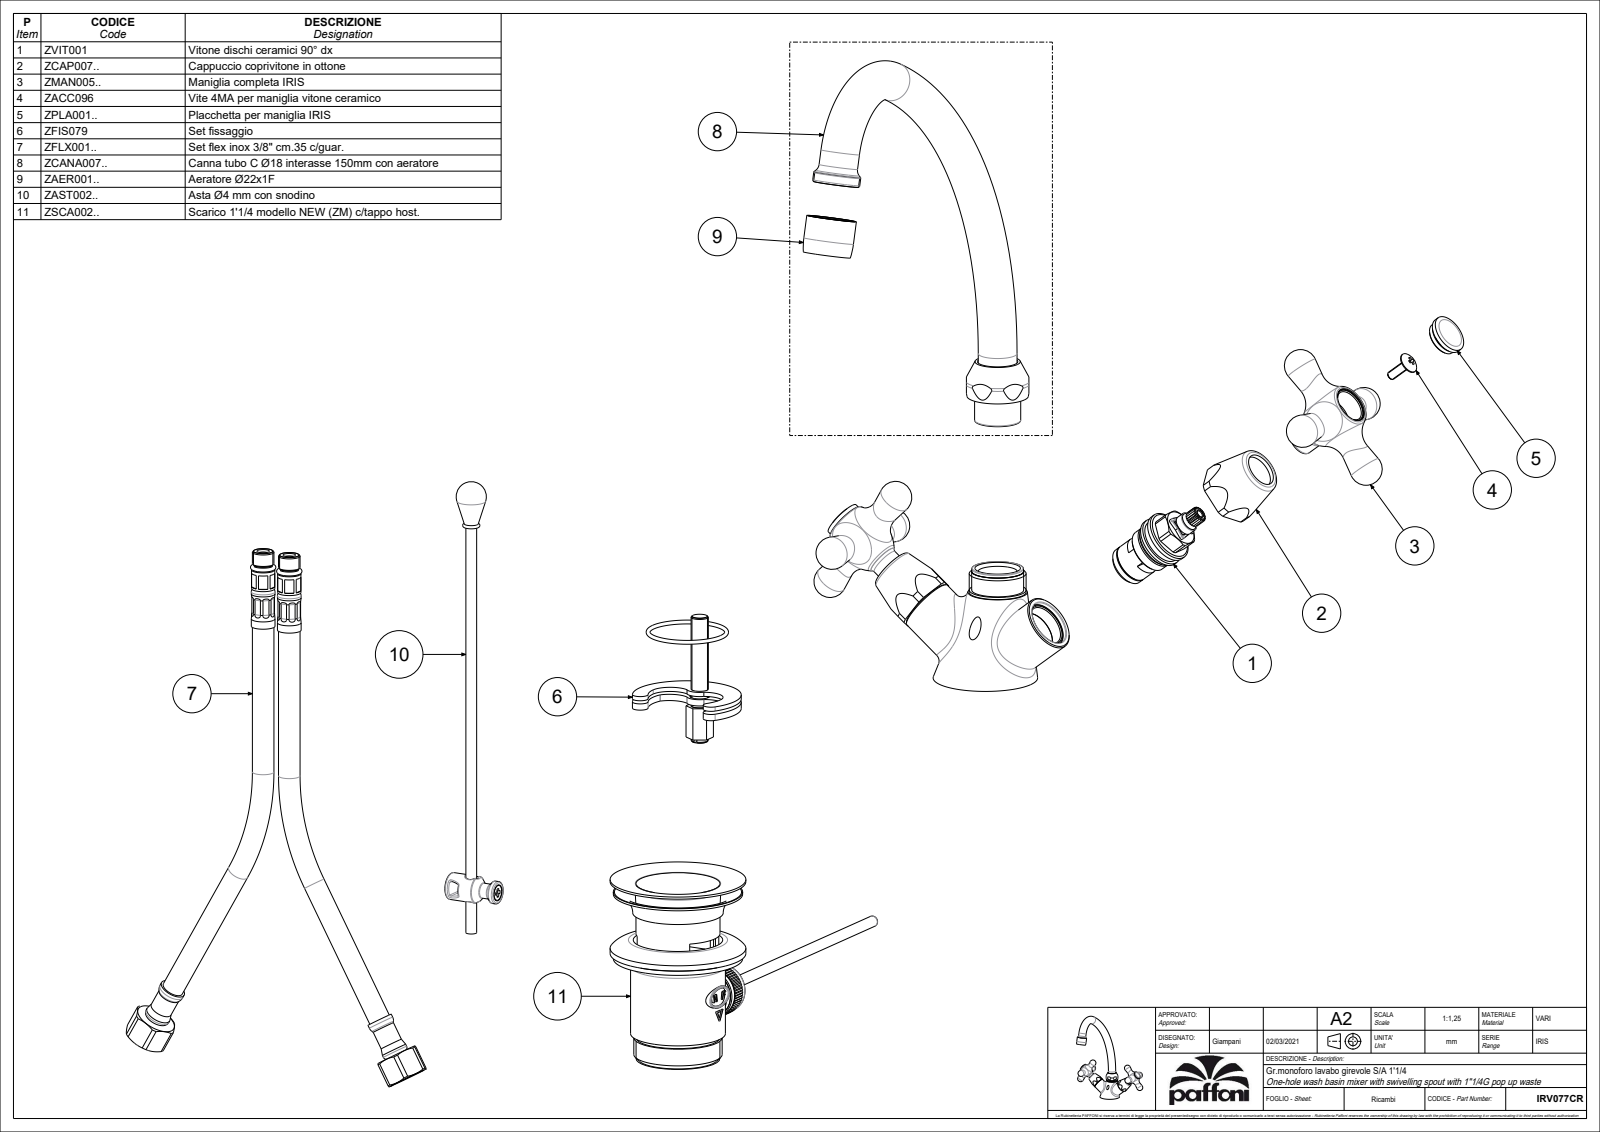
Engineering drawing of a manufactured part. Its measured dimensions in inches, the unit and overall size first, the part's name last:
Units: inches
Overall size (bounding box): 8.996 × 7.513 × 7.243
Round holes (diameter × count): ⌀0.008 ×777, ⌀0.354 ×4, ⌀0.827 ×3, ⌀0.181 ×2, ⌀0.346 ×2, ⌀0.406 ×2, ⌀0.433 ×2, ⌀0.618 ×2, ⌀0.646 ×2, ⌀0.748 ×2, ⌀0.906 ×2, ⌀0.217 ×1
Round bosses / shafts (diameter × count): ⌀0.709 ×4, ⌀1.035 ×2, ⌀0.732 ×2, ⌀0.693 ×2, ⌀0.531 ×2, ⌀0.374 ×2, ⌀0.323 ×2, ⌀0.291 ×2
Partial cylindrical surfaces — rounded edges, fillets, slot ends (radius × count): R0.004 ×34, R0.02 ×4, R0.039 ×4, R0.197 ×2, R0.366 ×2, R0.37 ×2, R0.571 ×2
Main face-to-face distances: 0.051, 0.039, 0.177, 1.043, 1.035, 0.287, 0.291, 0.858, 0.185, 0.669
Hole centre spacings: 0.059, 0.138, 0.079, 0.02, 0.197, 0.118, 0.039, 0.157
Volume: 9.039 in³ · Surface area: 128.6 in²
Bodies: 3 solids, 2620 faces (560 planar, 1786 cylindrical, 274 other)
Part name (STEP PRODUCT): IRV077CR
STEP written by: CREO PARAMETRIC BY PTC INC, 2020044 (CONFIG_CONTROL_DESIGN)
